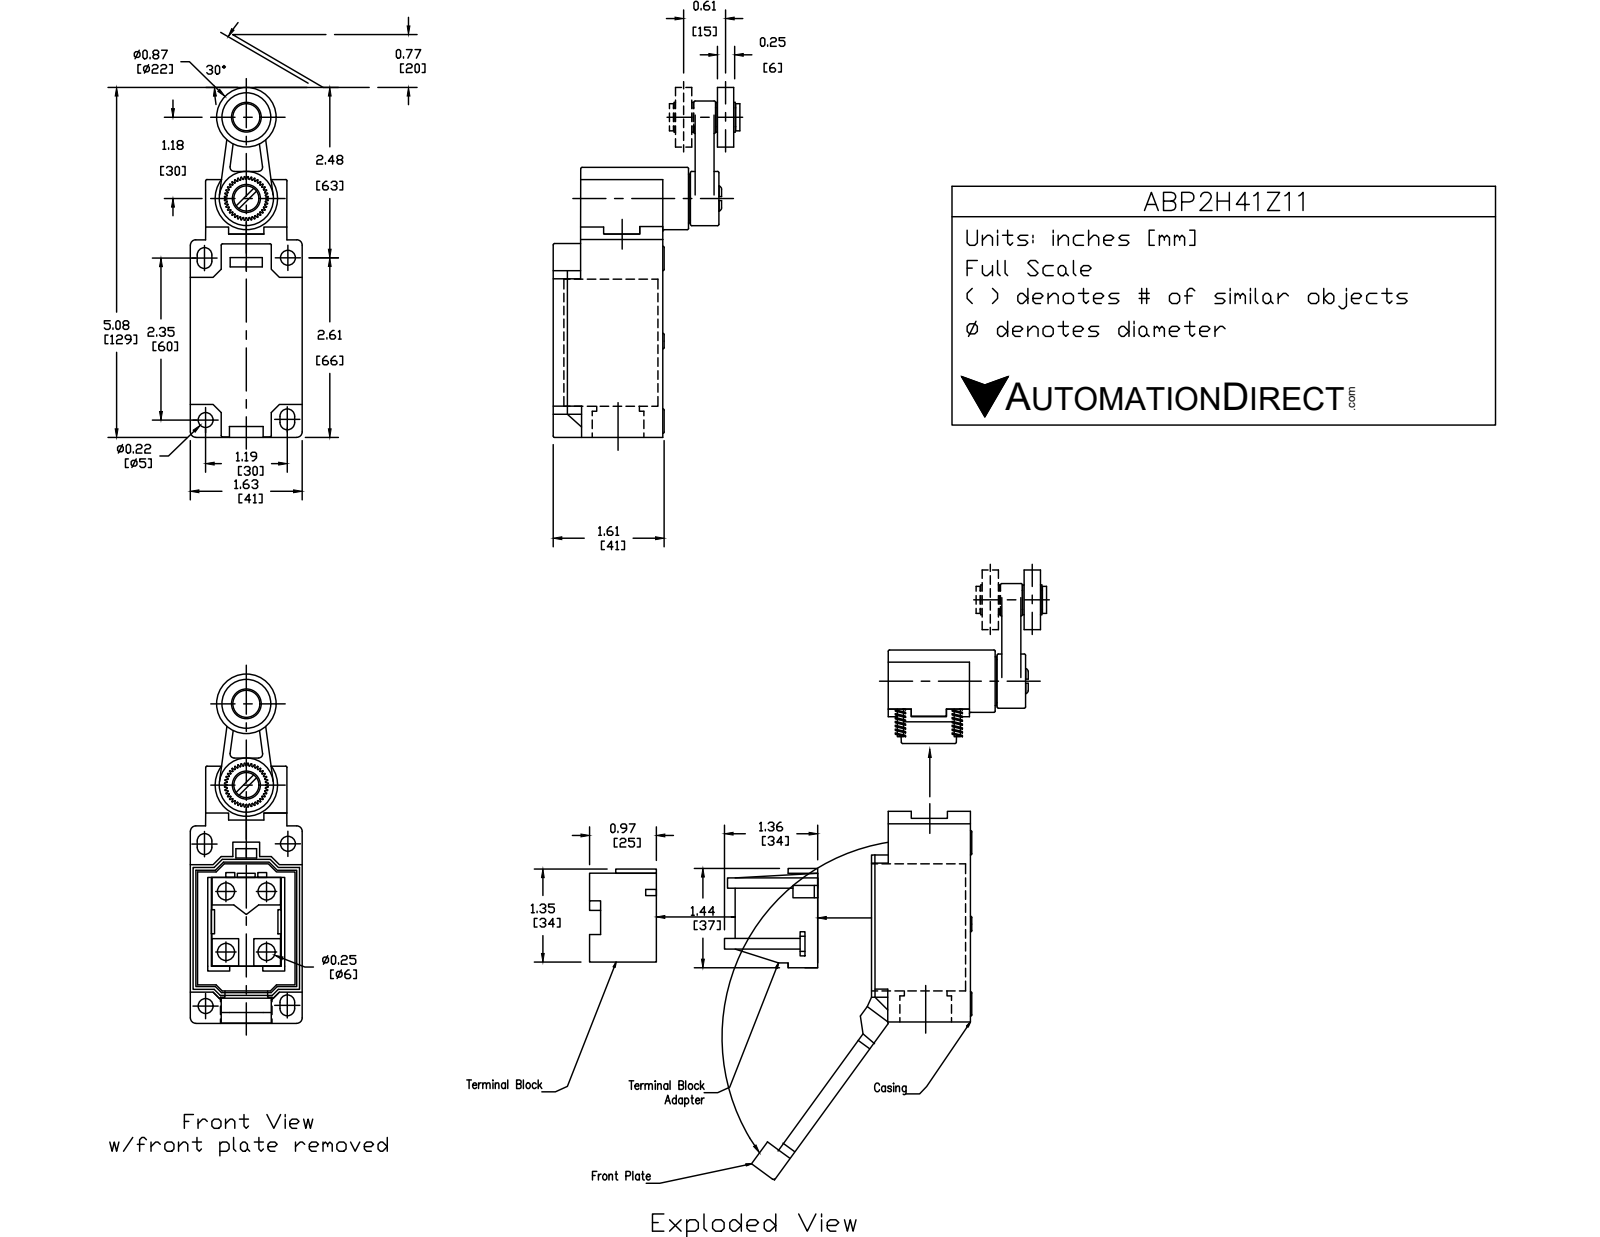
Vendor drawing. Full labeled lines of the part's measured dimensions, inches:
Part name (STEP PRODUCT): ABP2H41Z11
STEP written by: SolidWorks 2017 (AUTOMOTIVE_DESIGN)
Units: inches
Bodies: 5 solids, 193 faces (86 planar, 81 cylindrical, 26 other)
Overall size (bounding box): 5.091 × 2.313 × 1.614
Volume: 8.635 in³ · Surface area: 42.99 in²
Round holes (diameter × count): ⌀0.213 ×2, ⌀0.551 ×1, ⌀0.669 ×1, ⌀0.748 ×1
Round bosses / shafts (diameter × count): ⌀0.354 ×5, ⌀0.394 ×2, ⌀0.906 ×1, ⌀0.866 ×1, ⌀0.787 ×1, ⌀0.709 ×1, ⌀0.276 ×1
Partial cylindrical surfaces — rounded edges, fillets, slot ends (radius × count): R0.02 ×16, R0.079 ×4, R0.106 ×4, R0.236 ×1, R0.453 ×1, R0.472 ×1
Main face-to-face distances: 1.614, 1.565, 1.181, 0.217, 1.398, 2.972, 0.069, 0.384, 0.138, 0.354
Hole centre spacings: 1.042, 2.641, 3.274
